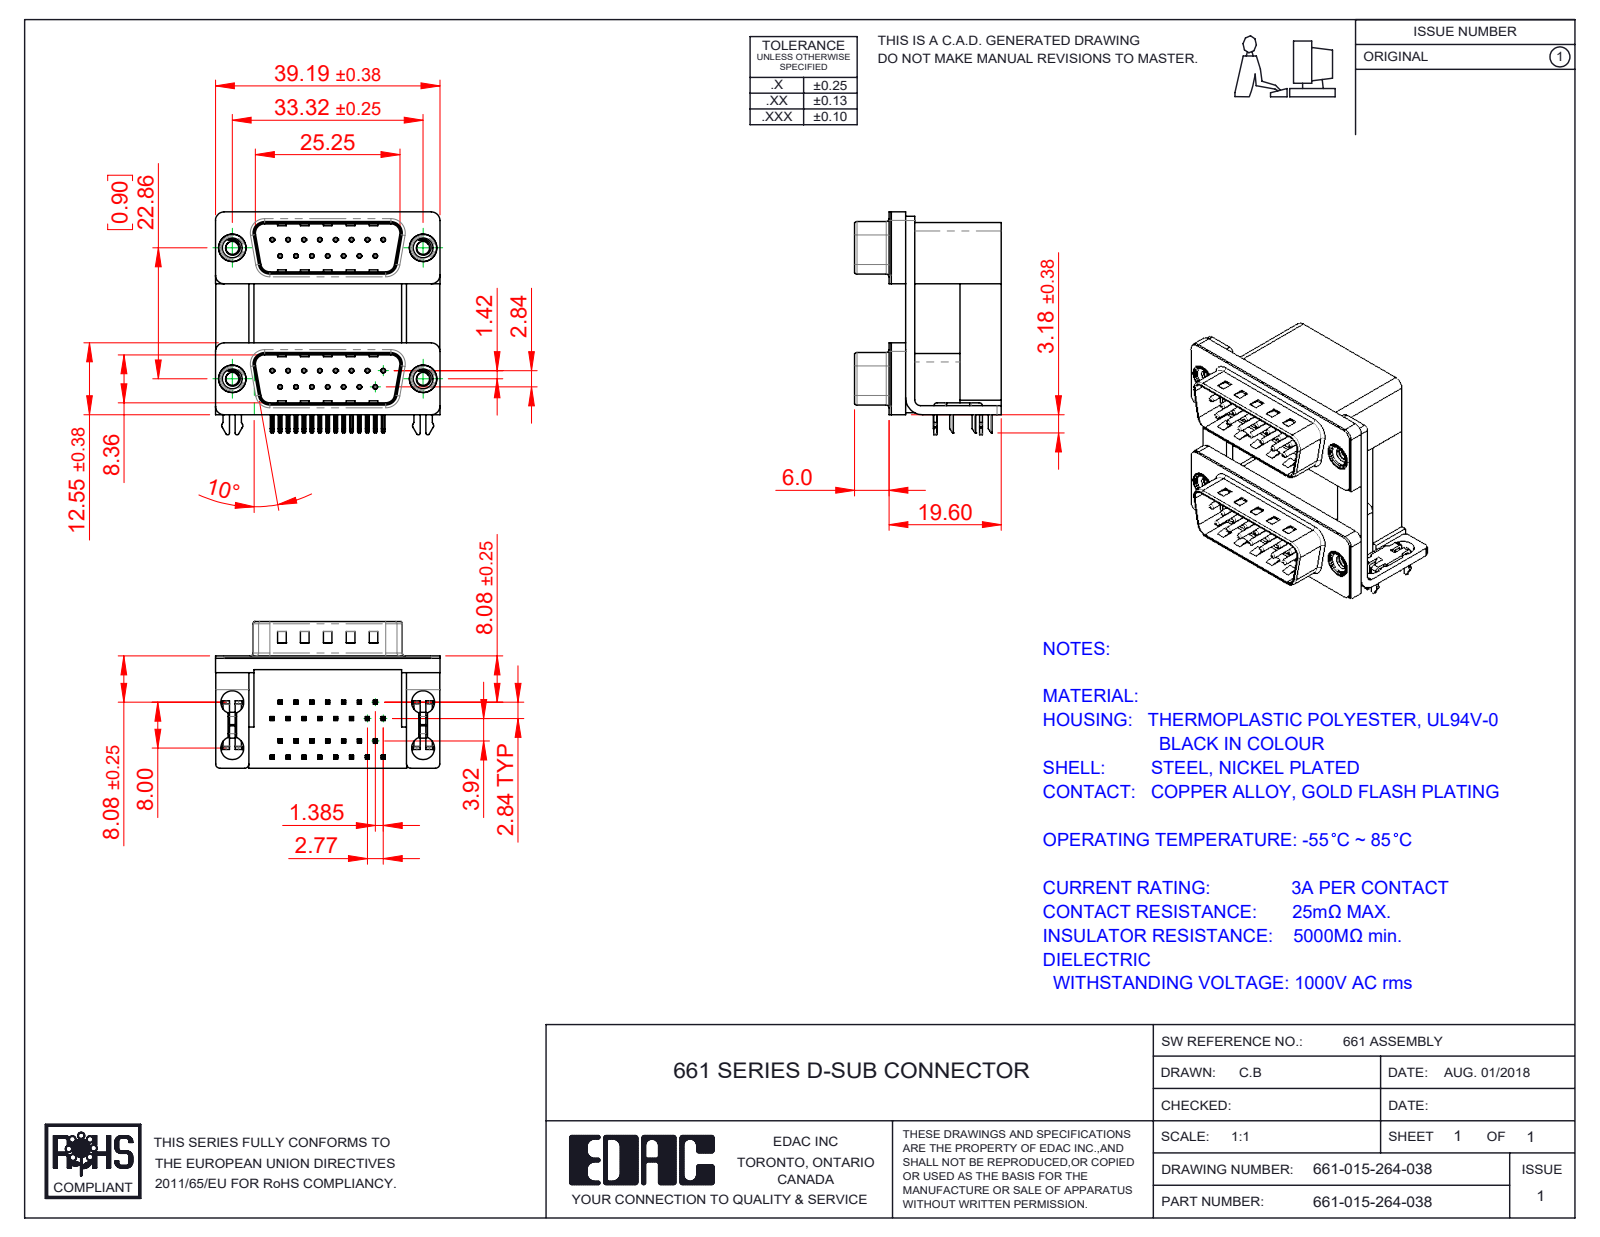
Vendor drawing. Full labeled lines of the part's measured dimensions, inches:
Part name (STEP PRODUCT): 661 Shell_15 Contacts; 661 Threaded Rivet_4-40; 661 Housing Lower_15 Contacts; 661 Contact Bottom Lower (+8 more)
STEP written by: SolidWorks 2020 (CONFIG_CONTROL_DESIGN)
Units: inches
Bodies: 43 solids, 3114 faces (1936 planar, 904 cylindrical, 274 other)
Overall size (bounding box): 1.543 × 1.532 × 1.008
Volume: 0.926 in³ · Surface area: 25.75 in²
Round holes (diameter × count): ⌀0.014 ×30, ⌀0.031 ×30, ⌀0.157 ×8, ⌀0.089 ×4, ⌀0.138 ×4, ⌀0.189 ×4, ⌀0.197 ×4
Round bosses / shafts (diameter × count): ⌀0.03 ×30, ⌀0.193 ×4, ⌀0.187 ×4, ⌀0.154 ×4
Partial cylindrical surfaces — rounded edges, fillets, slot ends (radius × count): R0.01 ×130, R0.005 ×60, R0.02 ×20, R0.059 ×16, R0.03 ×10, R0.035 ×8, R0.063 ×8, R0.079 ×8
Main face-to-face distances: 0.016, 0.472, 0.9, 0.756, 0.283, 0.657, 0.374, 0.098, 0.488, 0.421
Hole centre spacings: 0.124, 0.109, 0.907, 0.218, 0.926, 0.327, 0.957, 0.9
